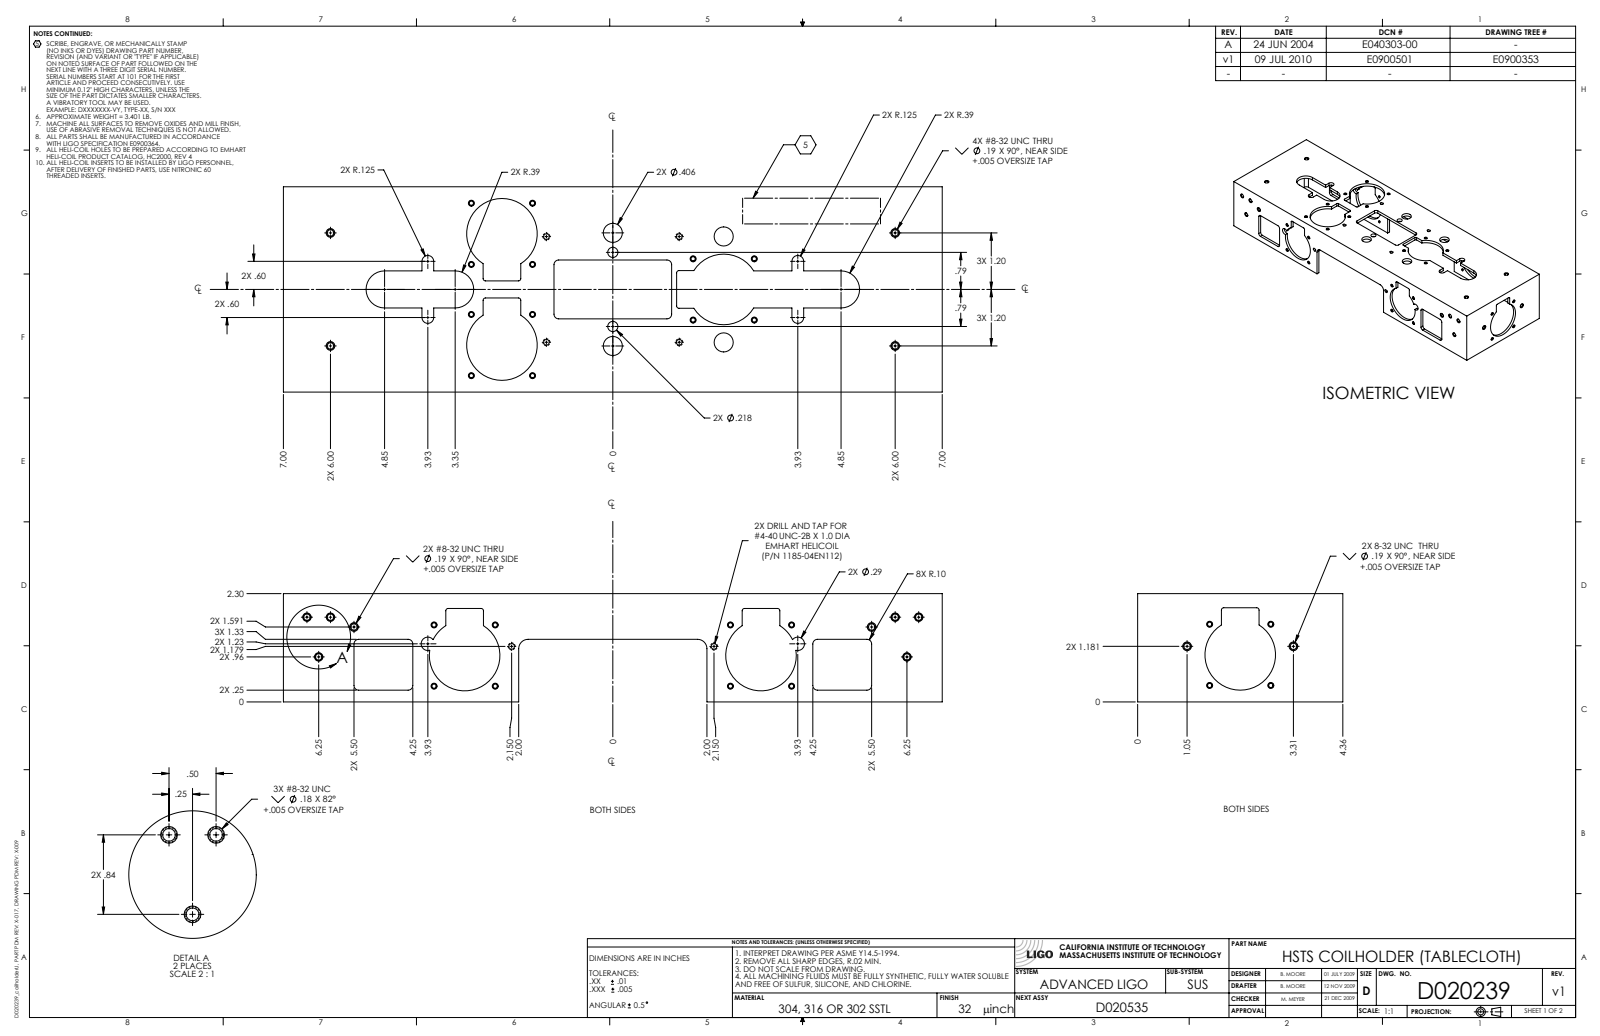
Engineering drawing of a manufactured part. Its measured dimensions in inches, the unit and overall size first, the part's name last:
Units: inches
Overall size (bounding box): 14 × 4.36 × 2.3
Round holes (diameter × count): ⌀0.089 ×24, ⌀0.136 ×14, ⌀0.12 ×6, ⌀0.406 ×4, ⌀1.5 ×3, ⌀0.218 ×2
Partial cylindrical surfaces — rounded edges, fillets, slot ends (radius × count): R0.05 ×12, R0.1 ×12, R0.125 ×12, R0.394 ×3, R0.75 ×3, R0.143 ×2, R0.2 ×2
Main face-to-face distances: 0.113, 0.125, 4.247, 4.36, 4.134, 13.887, 14, 13.774, 2.175, 2.3
Hole centre spacings: 1.3, 0.919, 1.839, 4.857, 2.362, 0.805, 0.88, 1.413
Volume: 11.76 in³ · Surface area: 211.9 in²
Bodies: 1 solid, 446 faces (81 planar, 241 cylindrical, 124 other)
Part name (STEP PRODUCT): D020239-v1_aLIGO_SUS_HSTS_COILHOLDER (TABLECLOTH)
STEP written by: SolidWorks 2010 (CONFIG_CONTROL_DESIGN)
